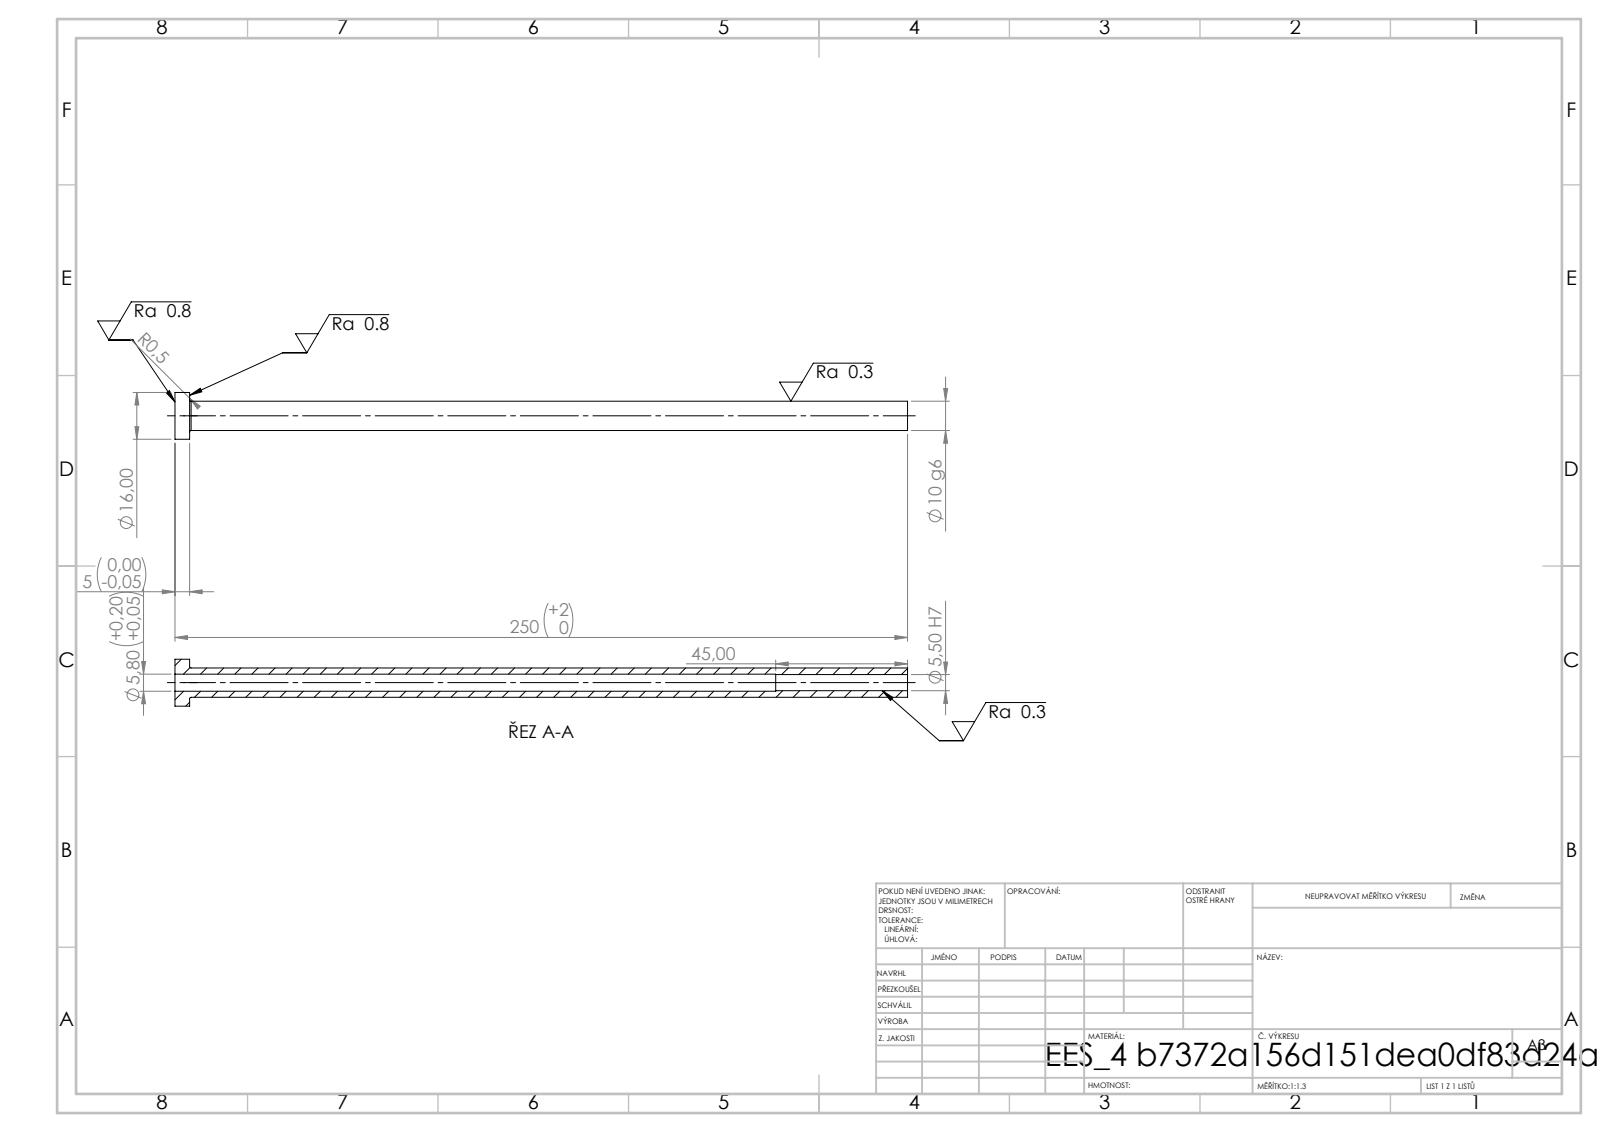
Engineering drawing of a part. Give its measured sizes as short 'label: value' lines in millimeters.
written by: SolidWorks 2019 (CONFIG_CONTROL_DESIGN)
unit: mm
bodies: 1 solid, 14 faces (4 planar, 8 cylindrical, 2 other)
size: 250 × 16 × 16
volume: 13 764 mm³; area: 12 809 mm²
holes: 1× ⌀5.5, 1× ⌀5.8
bosses: 1× ⌀16, 1× ⌀10
face distances: 5, 250, 245, 205, 200, 45
